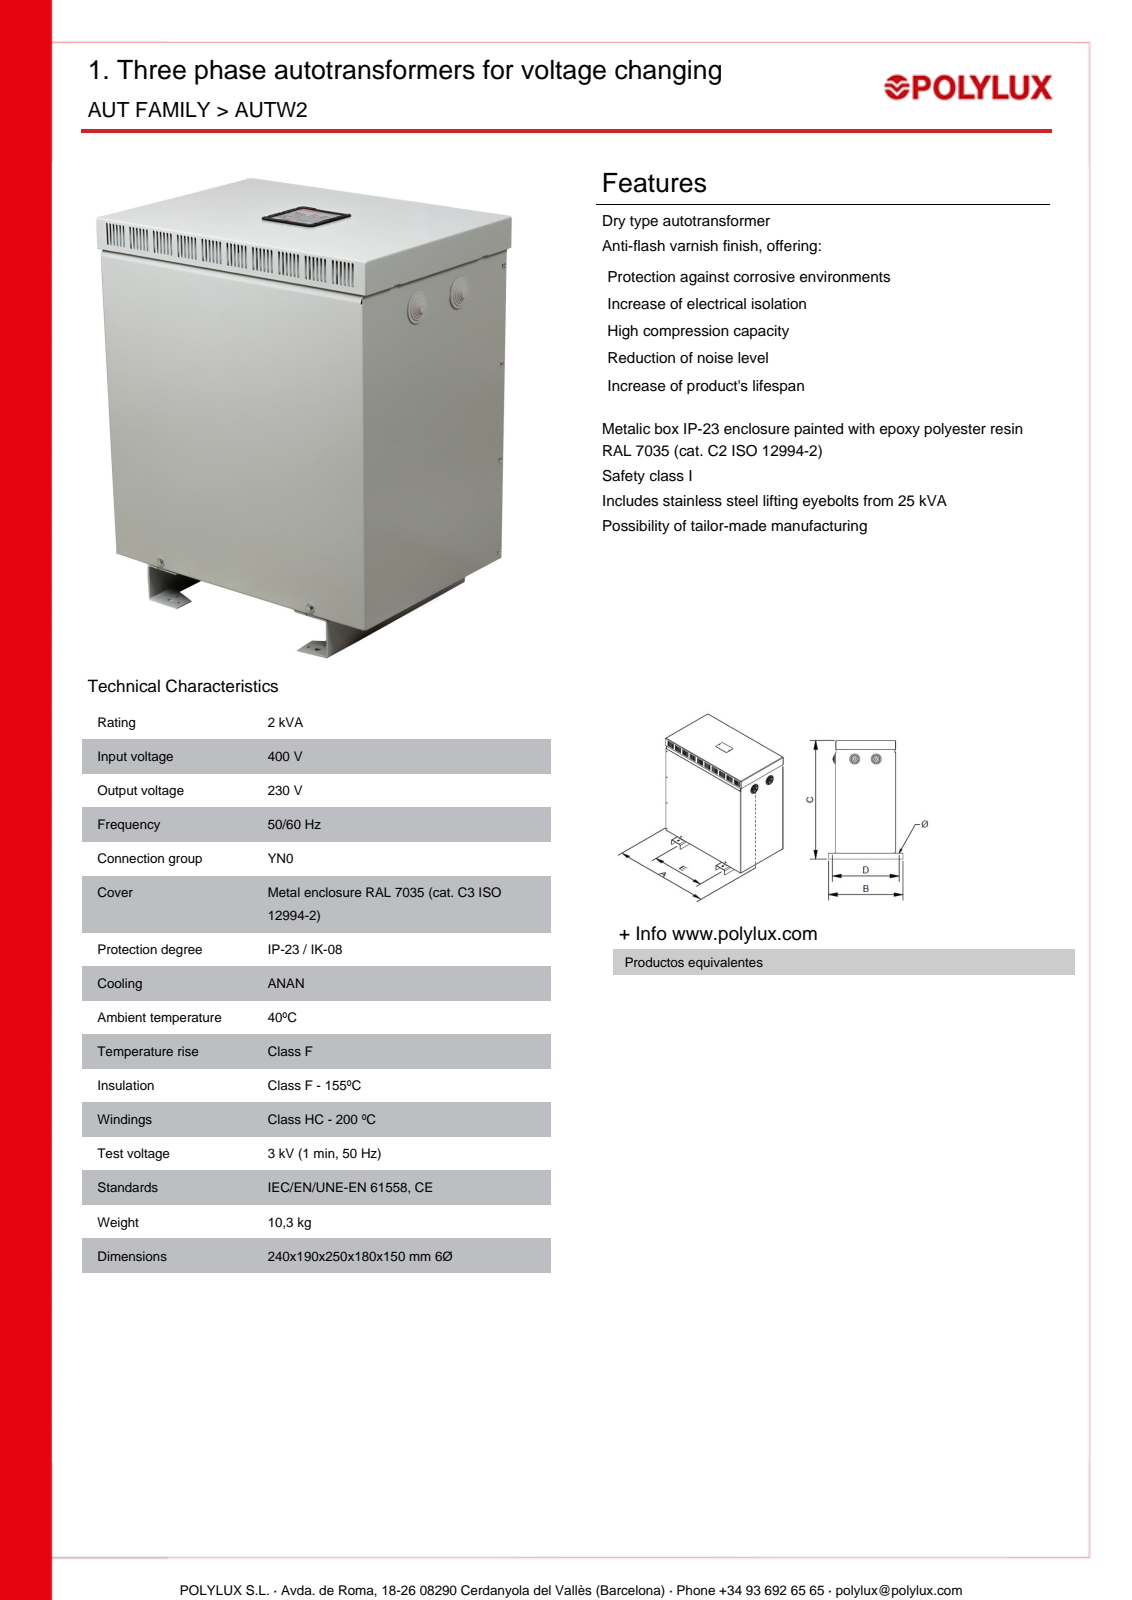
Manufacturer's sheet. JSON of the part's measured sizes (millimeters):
{"part_name": "AUTW2; Núcleo RC30x30; CAR0002T (30x30); BRI30-3IP02 (+8 more)", "step_written_by": "Autodesk Inventor 2018 (AUTOMOTIVE_DESIGN)", "units": "millimeters", "bodies": {"solids": 67, "faces": 3104, "planar": 2012, "cylindrical": 954, "other": 138}, "overall_size": [250.3, 243.04, 193.5], "volume_mm3": 1829000, "surface_area_mm2": 985828, "round_holes": [[4.3, 16], [6, 10], [7, 10], [4.92, 8], [3.5, 7], [4.13, 4], [5, 4], [5.6, 4], [6.4, 4], [3, 3], [4, 2], [16.5, 2]], "round_bosses_or_shafts": [[12, 4], [11, 4], [8.9, 4], [6.7, 4], [4.57, 4], [29.5, 2], [23.5, 2], [18.5, 2]], "partial_cylinders_radius": [[1.5, 83], [2, 28], [2.25, 24], [5, 20], [24.01, 16], [0.1, 12], [4.65, 12], [0.3, 11]], "face_to_face_distances": [1.5, 168.5, 233.5, 2, 1, 235, 32, 167, 170, 60], "hole_center_spacings": [6, 16.71, 12, 19.68, 18, 23.82, 15.6, 24]}
